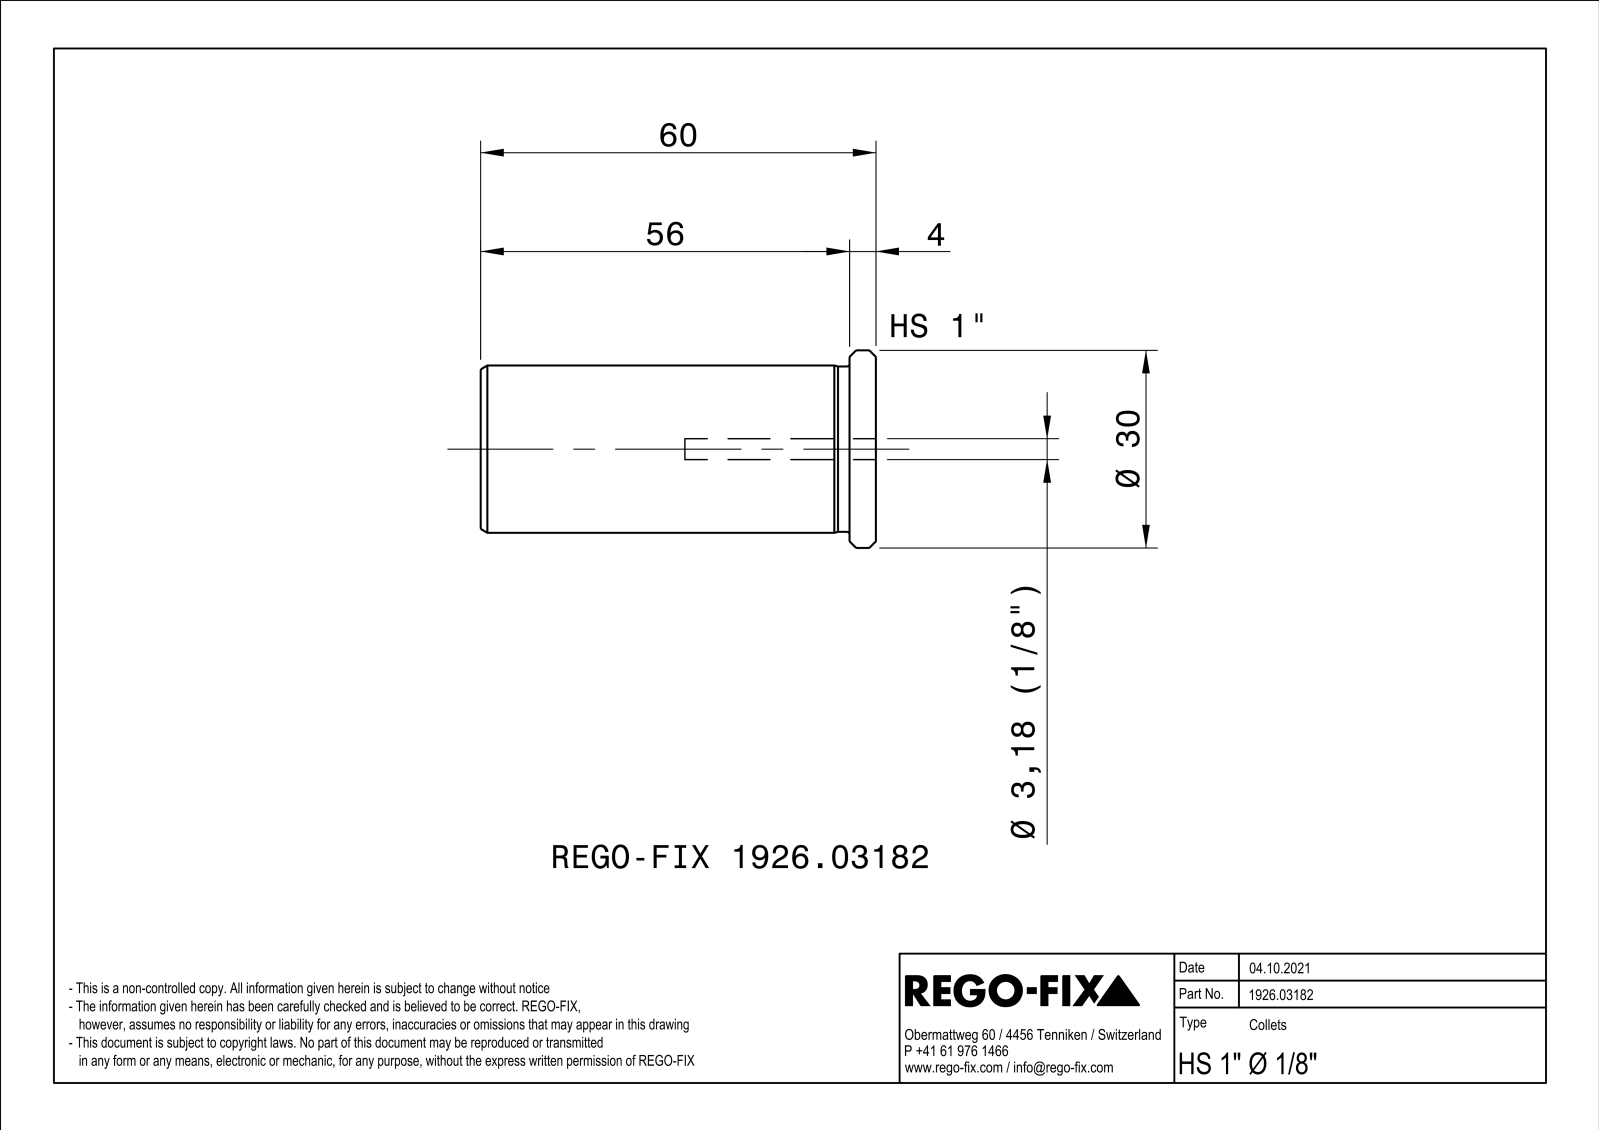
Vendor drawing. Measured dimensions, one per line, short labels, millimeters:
name: NOCUT
written by: SIEMENS PLM Software Solid Edge ST10 (AUTOMOTIVE_DESIGN)
unit: mm
bodies: 1 solid, 214 faces (131 planar, 13 cylindrical, 70 other)
size: 60 × 29.99 × 29.99
volume: 24 298 mm³; area: 10 433 mm²
holes: 1× ⌀3.17, 1× ⌀10, 1× ⌀20.5
bosses: 1× ⌀30, 1× ⌀25.4, 1× ⌀25.1
rounds: 1× R378.53
face distances: 0.8, 60, 4, 56, 3.95, 59.95, 1.52, 1.26, 1.01, 1.27
